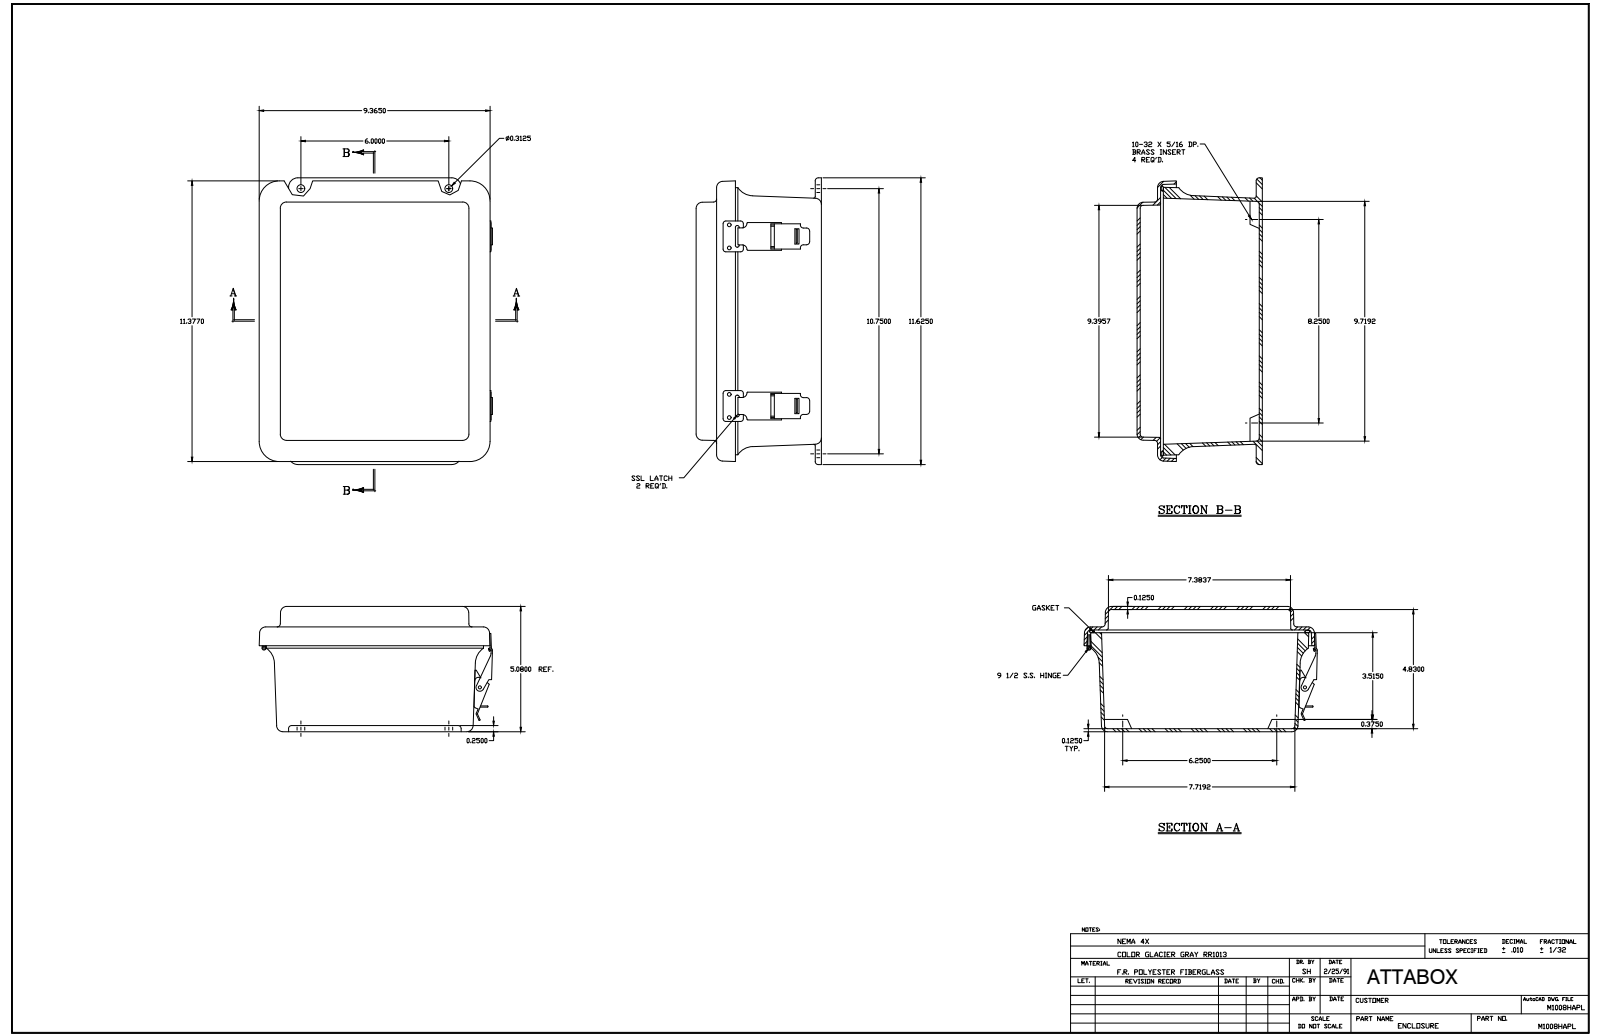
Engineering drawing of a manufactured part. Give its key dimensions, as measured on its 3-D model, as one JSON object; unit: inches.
{"part_name": "M1008HAPL", "step_written_by": "SolidWorks 2018 (AUTOMOTIVE_DESIGN)", "units": "inches", "bodies": {"solids": 38, "faces": 989, "planar": 409, "cylindrical": 409, "other": 171}, "overall_size": [11.625, 9.534, 5.063], "volume_in3": 62.77, "surface_area_in2": 884.2, "round_holes": [[0.14, 20], [0.104, 8], [0.131, 8], [0.152, 5], [0.13, 4], [0.156, 4], [0.218, 4], [0.135, 2], [0.375, 2], [0.085, 1], [0.085, 1]], "round_bosses_or_shafts": [[0.125, 12], [0.25, 8], [0.27, 4], [0.125, 4], [0.3, 1], [0.17, 1], [0.155, 1], [0.135, 1]], "partial_cylinders_radius": [[0.125, 32], [0.015, 20], [0.031, 20], [0.045, 16], [0.03, 12], [0.25, 12], [0.023, 8], [0.06, 6]], "face_to_face_distances": [0.125, 0.125, 4.813, 4.938, 5.063, 4.938, 4.109, 3.984, 0.829, 0.954], "hole_center_spacings": [7, 0.75, 7.04, 0.937, 6, 3, 0.25, 1.467]}
